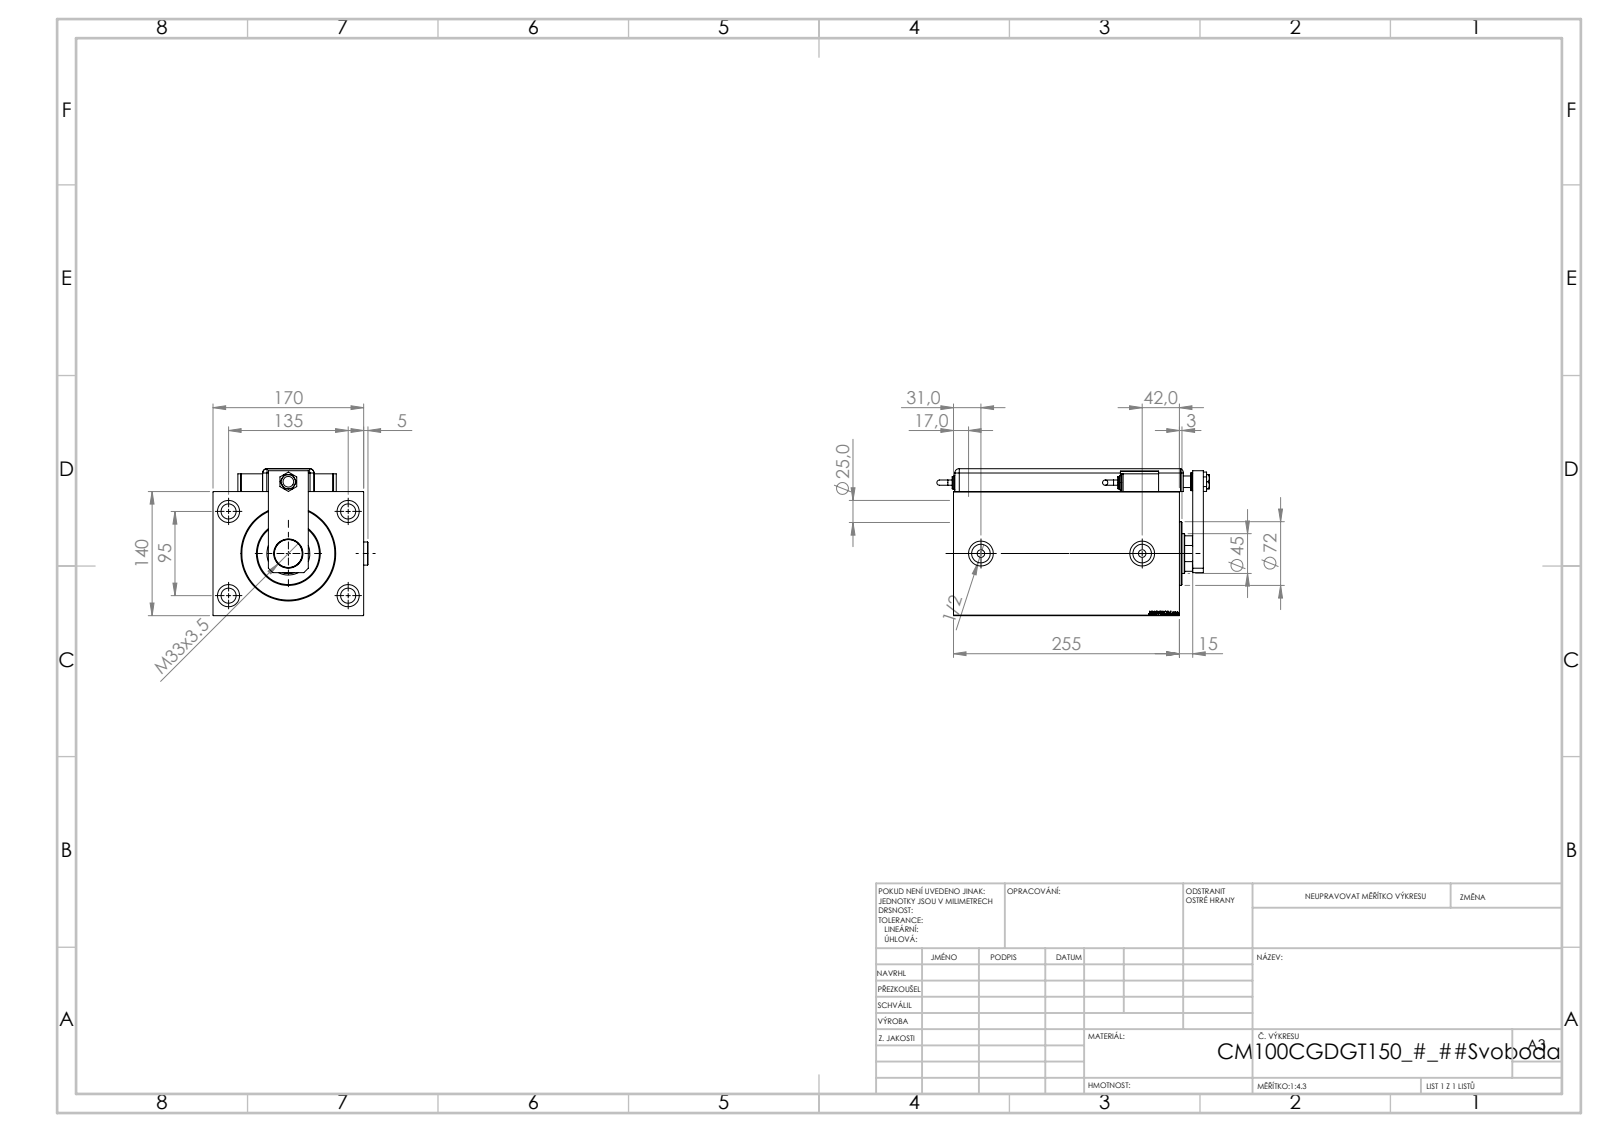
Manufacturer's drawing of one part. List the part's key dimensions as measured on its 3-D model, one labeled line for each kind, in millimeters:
Part name (STEP PRODUCT): V450CM_C_Body; ZARAZKA_Q; SWITCH DIM A_G; V450CM_C_VCP (+7 more)
STEP written by: SolidWorks 2019 (CONFIG_CONTROL_DESIGN)
Units: millimetres
Bodies: 15 solids, 1303 faces (649 planar, 133 cylindrical, 521 other)
Overall size (bounding box): 307.66 × 174.9 × 165.8
Volume: 5 090 000 mm³ · Surface area: 529 798 mm²
Round holes (diameter × count): ⌀17 ×4, ⌀25 ×4, ⌀4 ×2, ⌀8 ×2, ⌀8.5 ×2, ⌀20.96 ×2, ⌀28 ×2, ⌀12 ×1, ⌀13 ×1, ⌀14 ×1, ⌀31.5 ×1, ⌀33 ×1
Round bosses / shafts (diameter × count): ⌀20 ×3, ⌀26 ×2, ⌀16 ×2, ⌀14 ×2, ⌀6 ×2, ⌀72 ×1
Partial cylindrical surfaces — rounded edges, fillets, slot ends (radius × count): R5 ×9, R10 ×1, R22 ×1
Main face-to-face distances: 140, 170, 3, 255, 26, 229, 15, 25.8, 165.8, 162.8
Hole centre spacings: 82.54, 75.36, 95, 135, 145.15, 165.08, 20, 81
